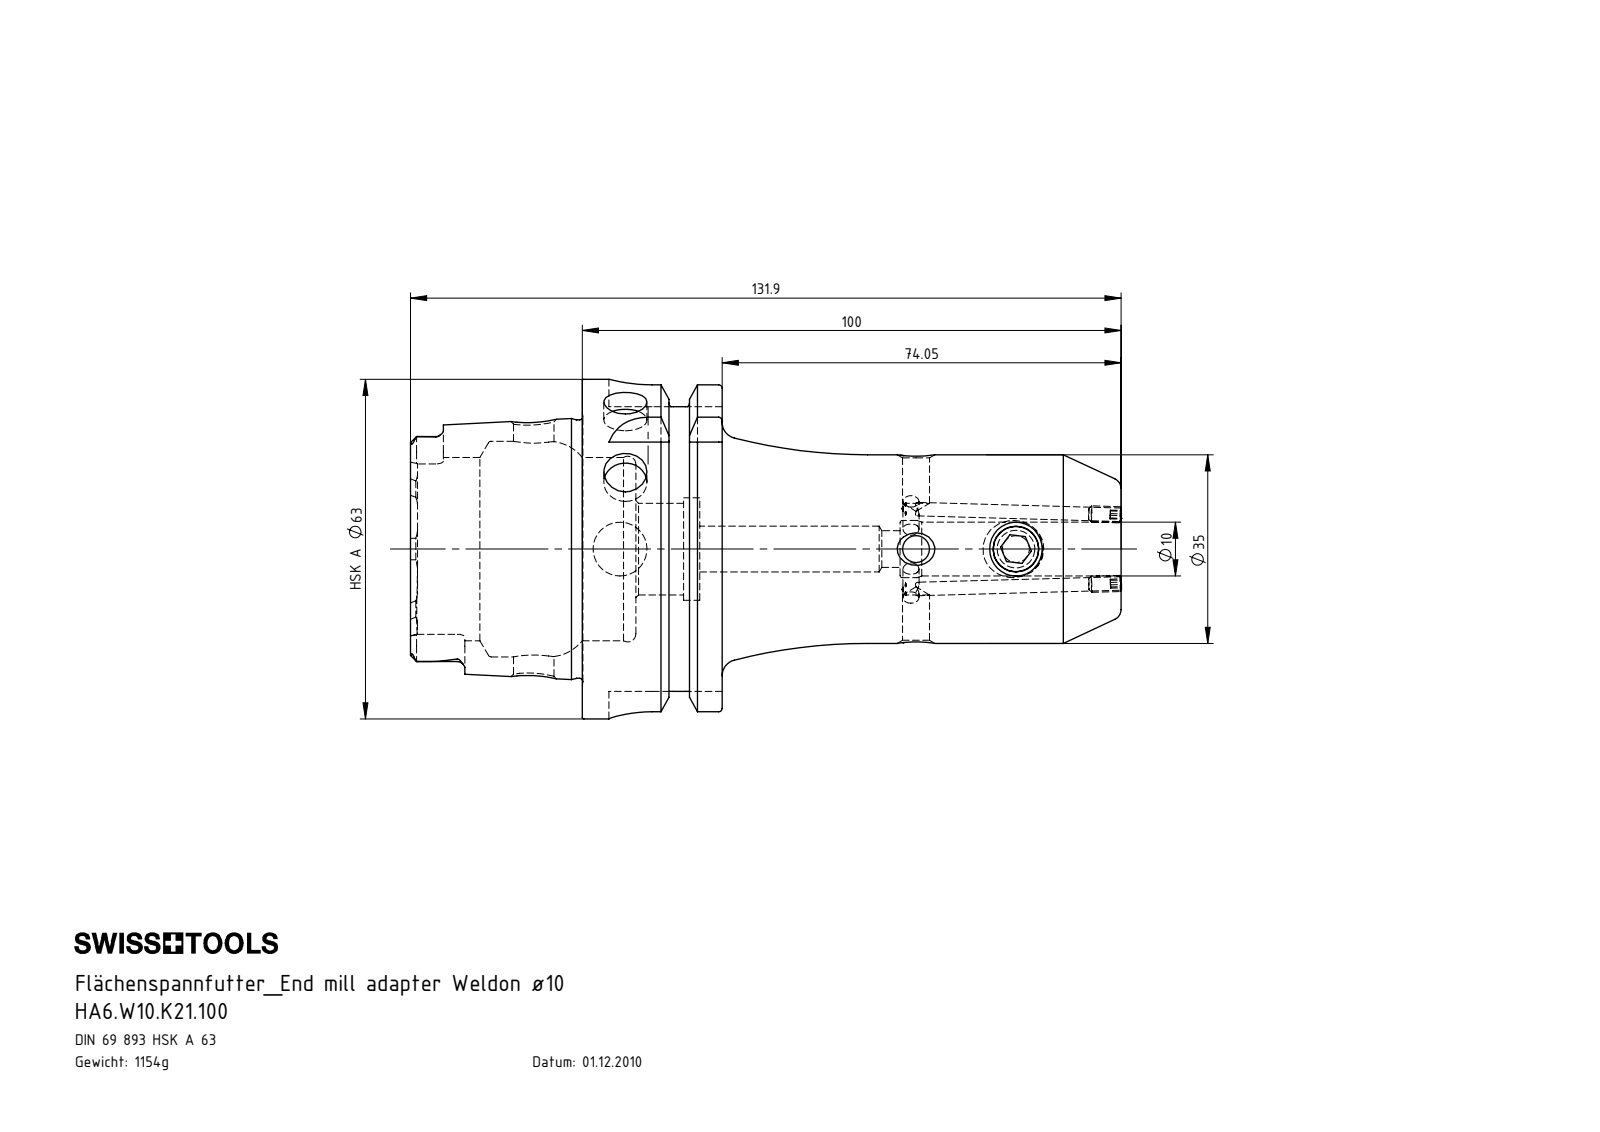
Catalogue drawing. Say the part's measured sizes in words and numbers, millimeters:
The part is named "W10-ER1.001.012; ERU-CJ2.001.006; HA6-W10.K21.100; HA6-W10.K21.100_C_Fertigbearbeitung". Its 3-D file was written by "SolidWorks 2012 (AUTOMOTIVE_DESIGN)". It is 4 solids with 292 faces: 77 planar, 83 cylindrical and 132 other. Overall it measures 131.98 by 63 by 63 millimeters. Its volume is 147 039 cubic millimeters and its surface area 34 188 square millimeters. Round holes: 2 of diameter 2.5, 2 of diameter 5, 2 of diameter 8, 2 of diameter 8.5, 2 of diameter 10, 1 of diameter 3, 1 of diameter 6.8, 1 of diameter 7.5, 1 of diameter 10.6, 1 of diameter 17, 1 of diameter 19, 1 of diameter 34. Round bosses or shafts: 2 of diameter 3, 1 of diameter 63, 1 of diameter 54.95, 1 of diameter 47.94, 1 of diameter 35, 1 of diameter 10. Partial cylindrical surfaces (rounded edges, fillets, slot ends): 6 of radius 1.4, 4 of radius 2.88, 4 of radius 8. The main face-to-face distances are 25.95, 16, 9.95, 31.9, 41.85, 57.85, 52.8, 131.9, 100, 90.05. The hole center spacings are 18.55, 54.95, 70.95, 73.5.
